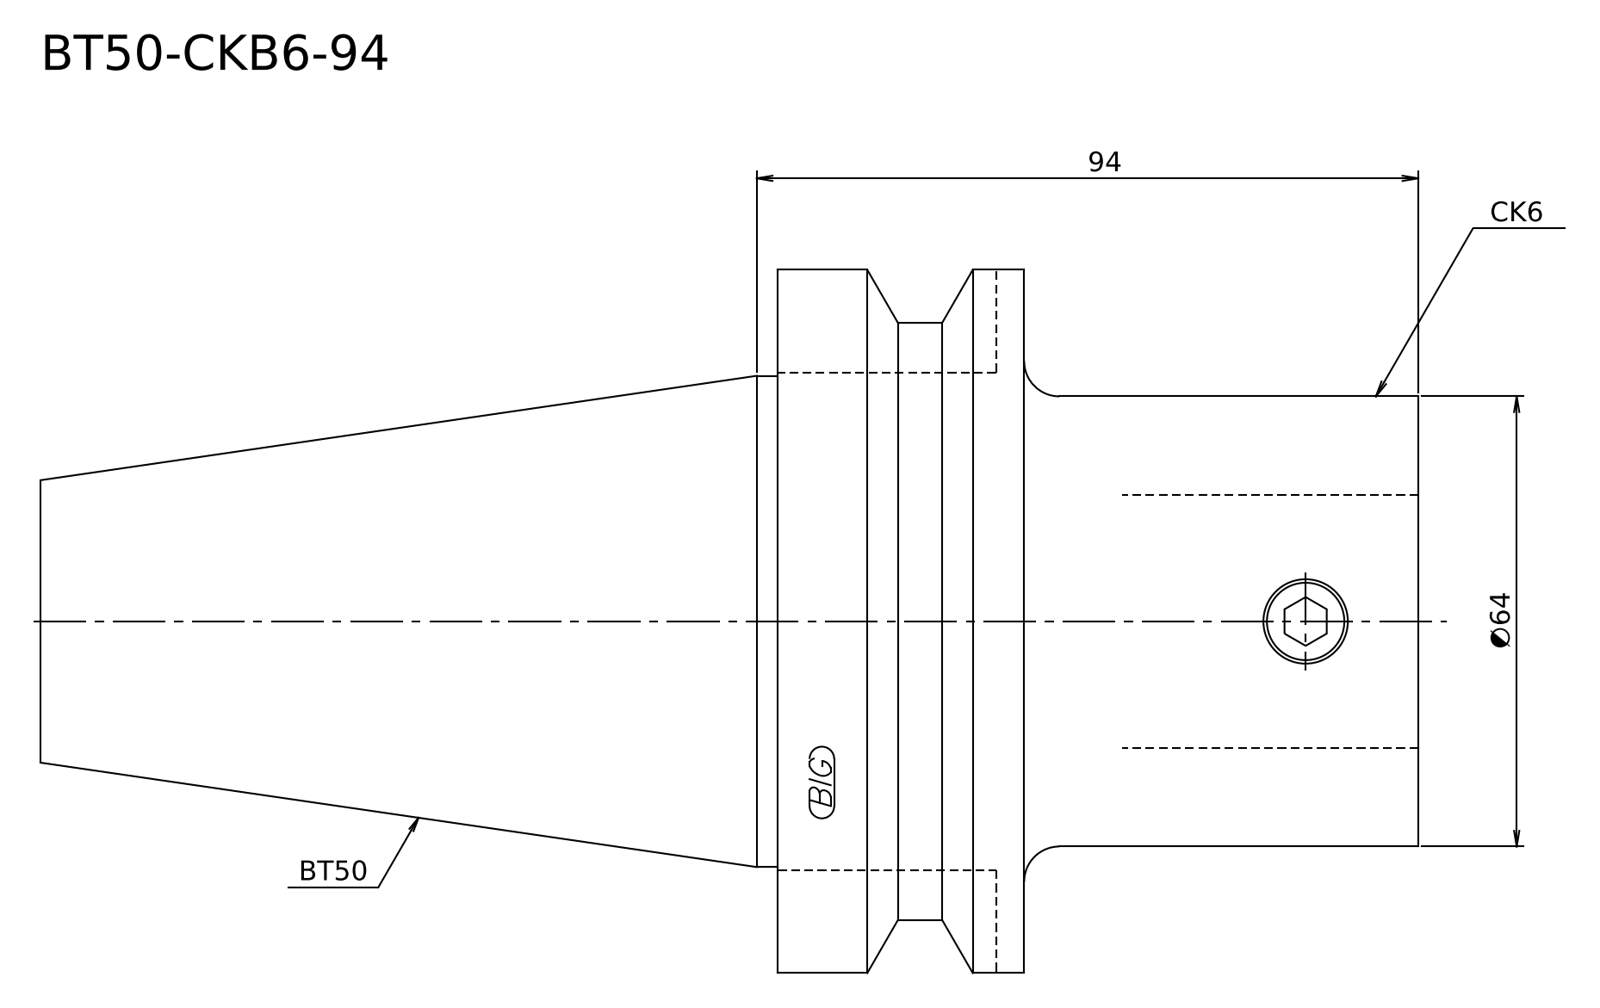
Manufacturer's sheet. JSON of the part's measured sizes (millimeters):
{"step_written_by": "Kubotek KeyCreator V8.5.1 (14335) (CONFIG_CONTROL_DESIGN)", "units": "millimeters", "bodies": {"solids": 1, "faces": 13, "planar": 4, "cylindrical": 5, "other": 4}, "overall_size": [195.8, 100, 100], "volume_mm3": 693441, "surface_area_mm2": 55291, "round_bosses_or_shafts": [[100, 1], [85, 1], [69.85, 1], [64, 1]], "face_to_face_distances": [35, 56, 91, 195.8, 139.8, 104.8]}
